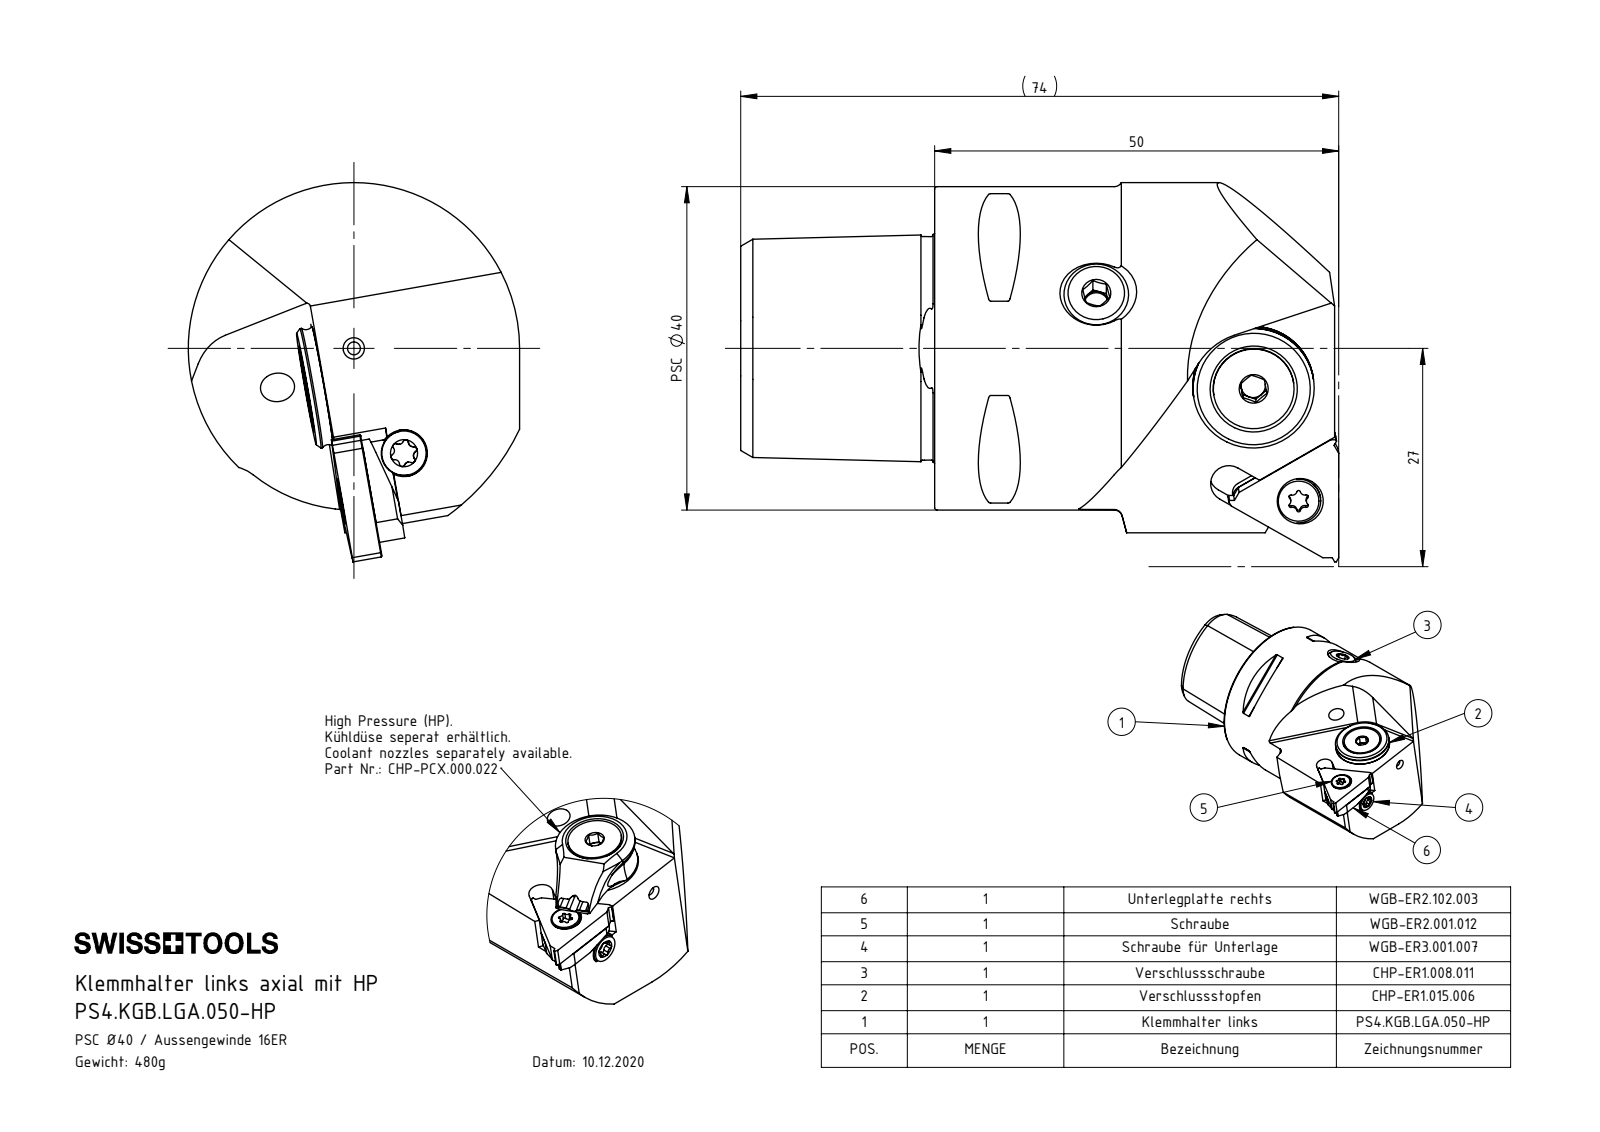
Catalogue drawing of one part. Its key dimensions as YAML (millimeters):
part_name: "CHP-ER1.015.006_A; LT16ER; WGB-ER3.001.007_A; CHP-ER1.015.006 (+8 more)"
step_written_by: "SolidWorks 2017 (AUTOMOTIVE_DESIGN)"
units: millimeters
bodies: {solids: 10, faces: 442, planar: 126, cylindrical: 132, other: 184}
overall_size: [74, 46.91, 41]
volume: 59988
surface_area: 16927
round_holes:
  - {diameter: 4.2, count: 3}
  - {diameter: 2.58, count: 2}
  - {diameter: 4, count: 2}
  - {diameter: 1.2, count: 1}
  - {diameter: 1.6, count: 1}
  - {diameter: 2, count: 1}
  - {diameter: 2.5, count: 1}
  - {diameter: 3, count: 1}
  - {diameter: 4.02, count: 1}
  - {diameter: 4.6, count: 1}
  - {diameter: 5, count: 1}
  - {diameter: 5.2, count: 1}
round_bosses_or_shafts:
  - {diameter: 5.5, count: 3}
  - {diameter: 40, count: 1}
  - {diameter: 15, count: 1}
  - {diameter: 13.4, count: 1}
  - {diameter: 10, count: 1}
  - {diameter: 8, count: 1}
  - {diameter: 5, count: 1}
  - {diameter: 3.18, count: 1}
partial_cylinders:
  - {radius: 0.3, count: 8}
  - {radius: 0.23, count: 6}
  - {radius: 0.34, count: 6}
  - {radius: 0.57, count: 6}
  - {radius: 0.57, count: 6}
  - {radius: 0.1, count: 2}
  - {radius: 0.5, count: 2}
  - {radius: 0.25, count: 1}
face_to_face_distances: [4.79, 24, 3.2, 15.52, 5.1, 0.31, 1.46, 3.33, 3.64, 1.74]
hole_center_spacings: [4.5, 2, 4.46, 4.47, 4.48, 4.53, 8.64, 8.66]
